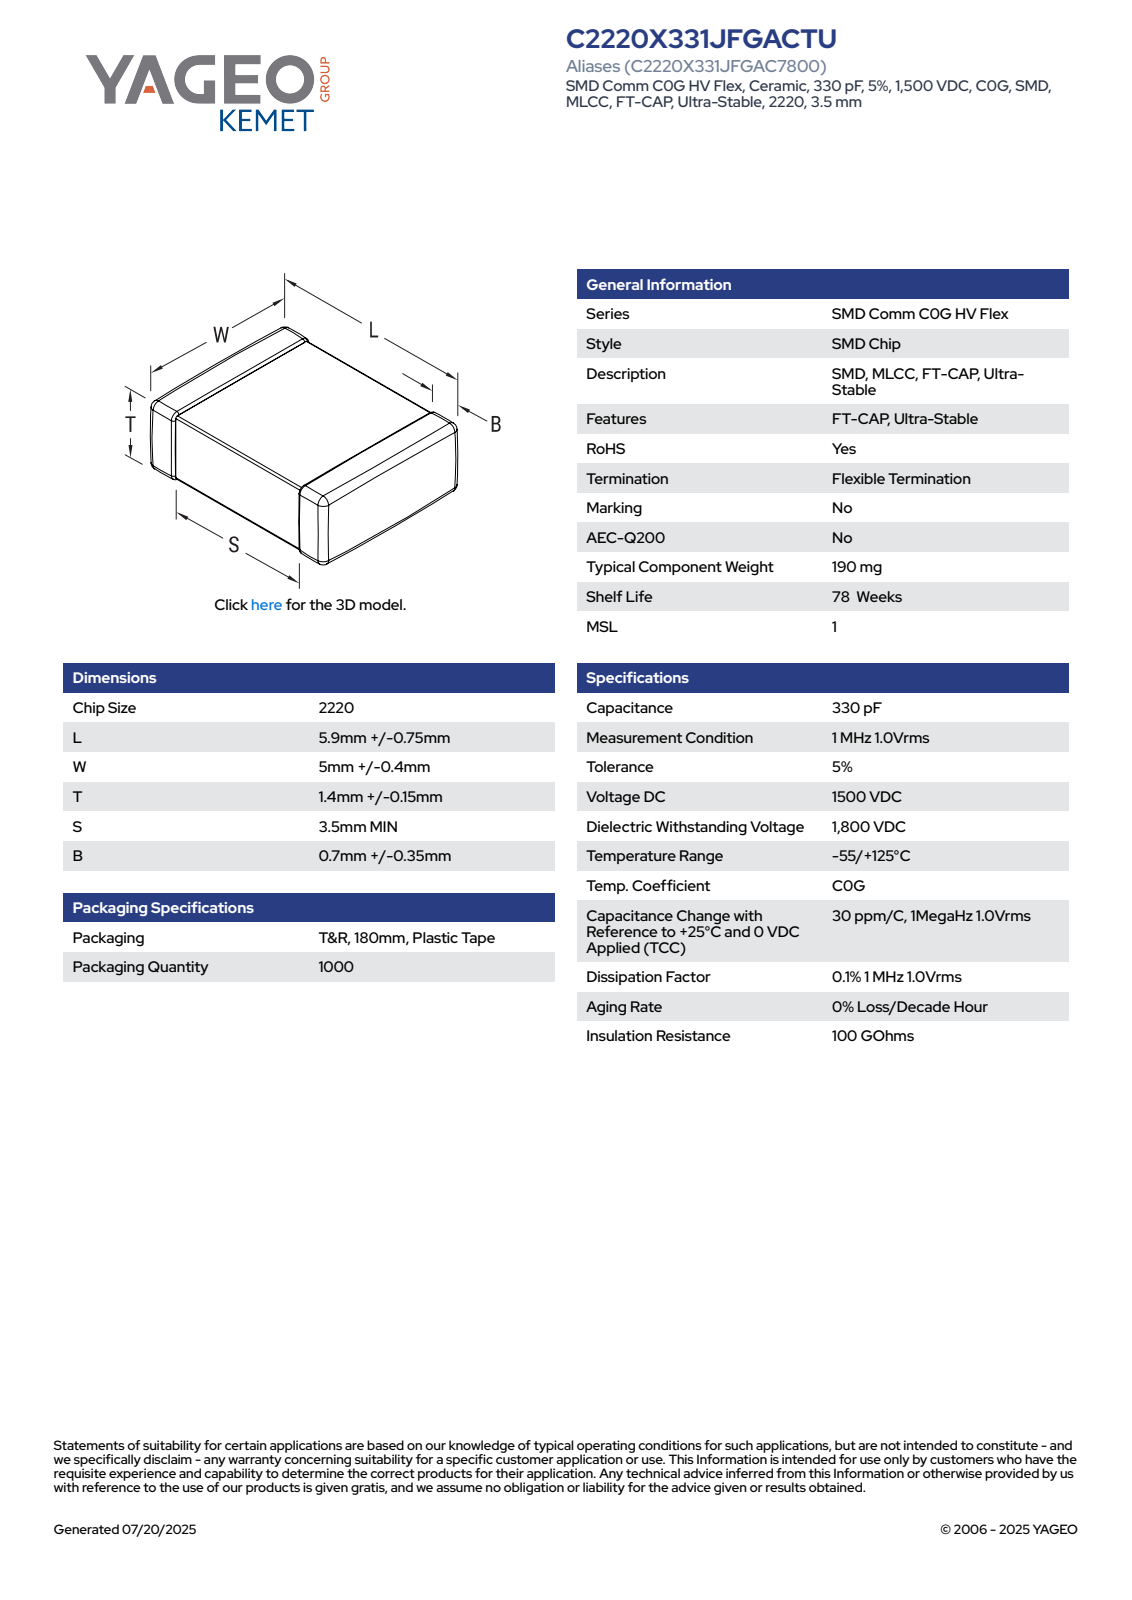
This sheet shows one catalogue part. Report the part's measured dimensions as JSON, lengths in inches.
{"part_name": "CCS_CCSTDNOS_2220_L6.65W5.4T1.55B1.05", "step_written_by": "SolidWorks 2014 (AUTOMOTIVE_DESIGN)", "units": "inches", "bodies": {"solids": 4, "faces": 121, "planar": 71, "cylindrical": 34, "other": 16}, "overall_size": [0.262, 0.213, 0.061], "volume_in3": 0.003, "surface_area_in2": 0.164, "partial_cylinders_radius": [[0.004, 24]], "face_to_face_distances": [0.052, 0.057, 0.061, 0.262, 0.204, 0.208, 0.213, 0.099, 0.109, 0.103]}
